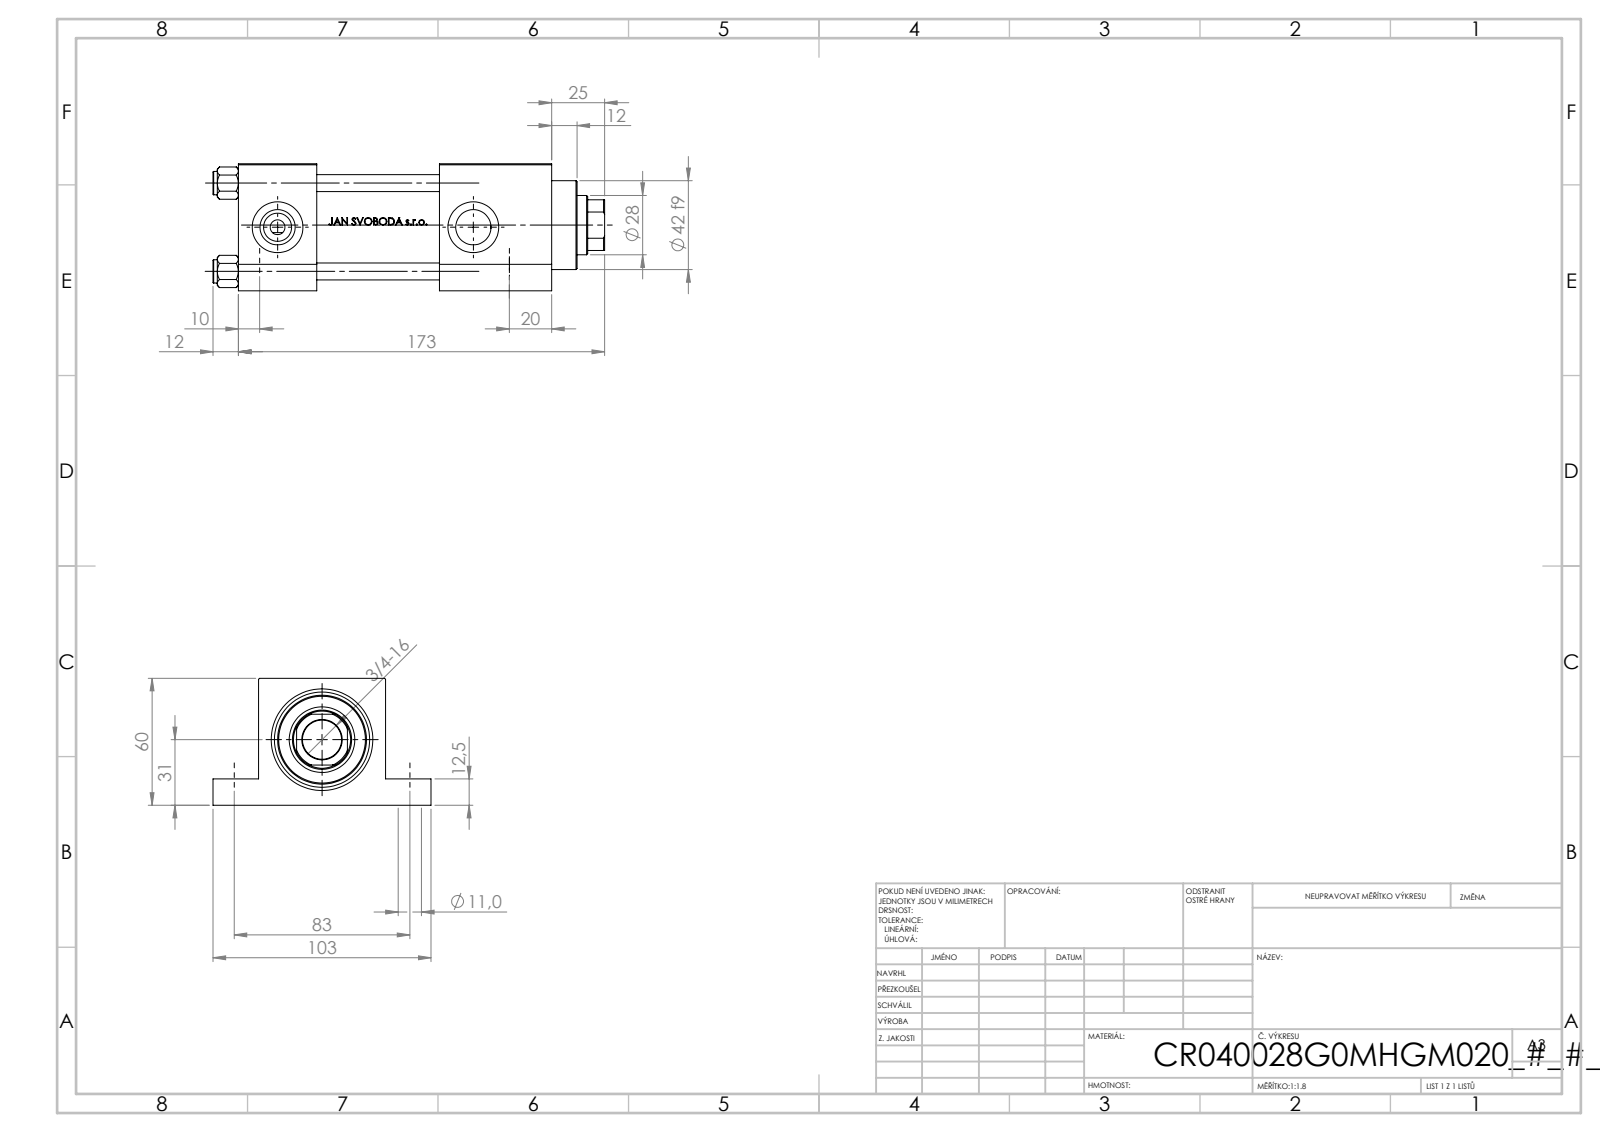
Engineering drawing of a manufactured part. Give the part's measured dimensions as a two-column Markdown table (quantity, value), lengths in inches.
| quantity | value |
| --- | --- |
| part name | V215CR_G_TYCINKA; NUT_M5_G; V215CR_VCP_G; V215CR_G_Body (+1 more) |
| STEP written by | SolidWorks 2019 (CONFIG_CONTROL_DESIGN) |
| units | inches |
| bodies | 11 solids, 1087 faces (431 planar, 124 cylindrical, 532 other) |
| overall size | 7.283 × 4.055 × 2.362 |
| volume | 28.79 in³ |
| surface area | 186.4 in² |
| round holes (diameter × count) | 0.315 × 4, 0.433 × 4, 0.276 × 2, 0.656 × 2, 0.945 × 2, 0.728 × 1, 1.102 × 1, 1.22 × 1, 1.575 × 1, 1.772 × 1 |
| round bosses / shafts (diameter × count) | 0.433 × 4, 1.811 × 1, 1.654 × 1 |
| partial cylindrical surfaces (radius × count) | 0.531 × 1 |
| main face-to-face distances | 2.362, 1.457, 0.492, 1.87, 3.74, 2.283, 5.827, 4.37, 2.087, 0.846 |
| hole center spacings | 1.642, 1.133, 1.189, 2.322, 3.268, 4.646, 5.68, 3.642 |
